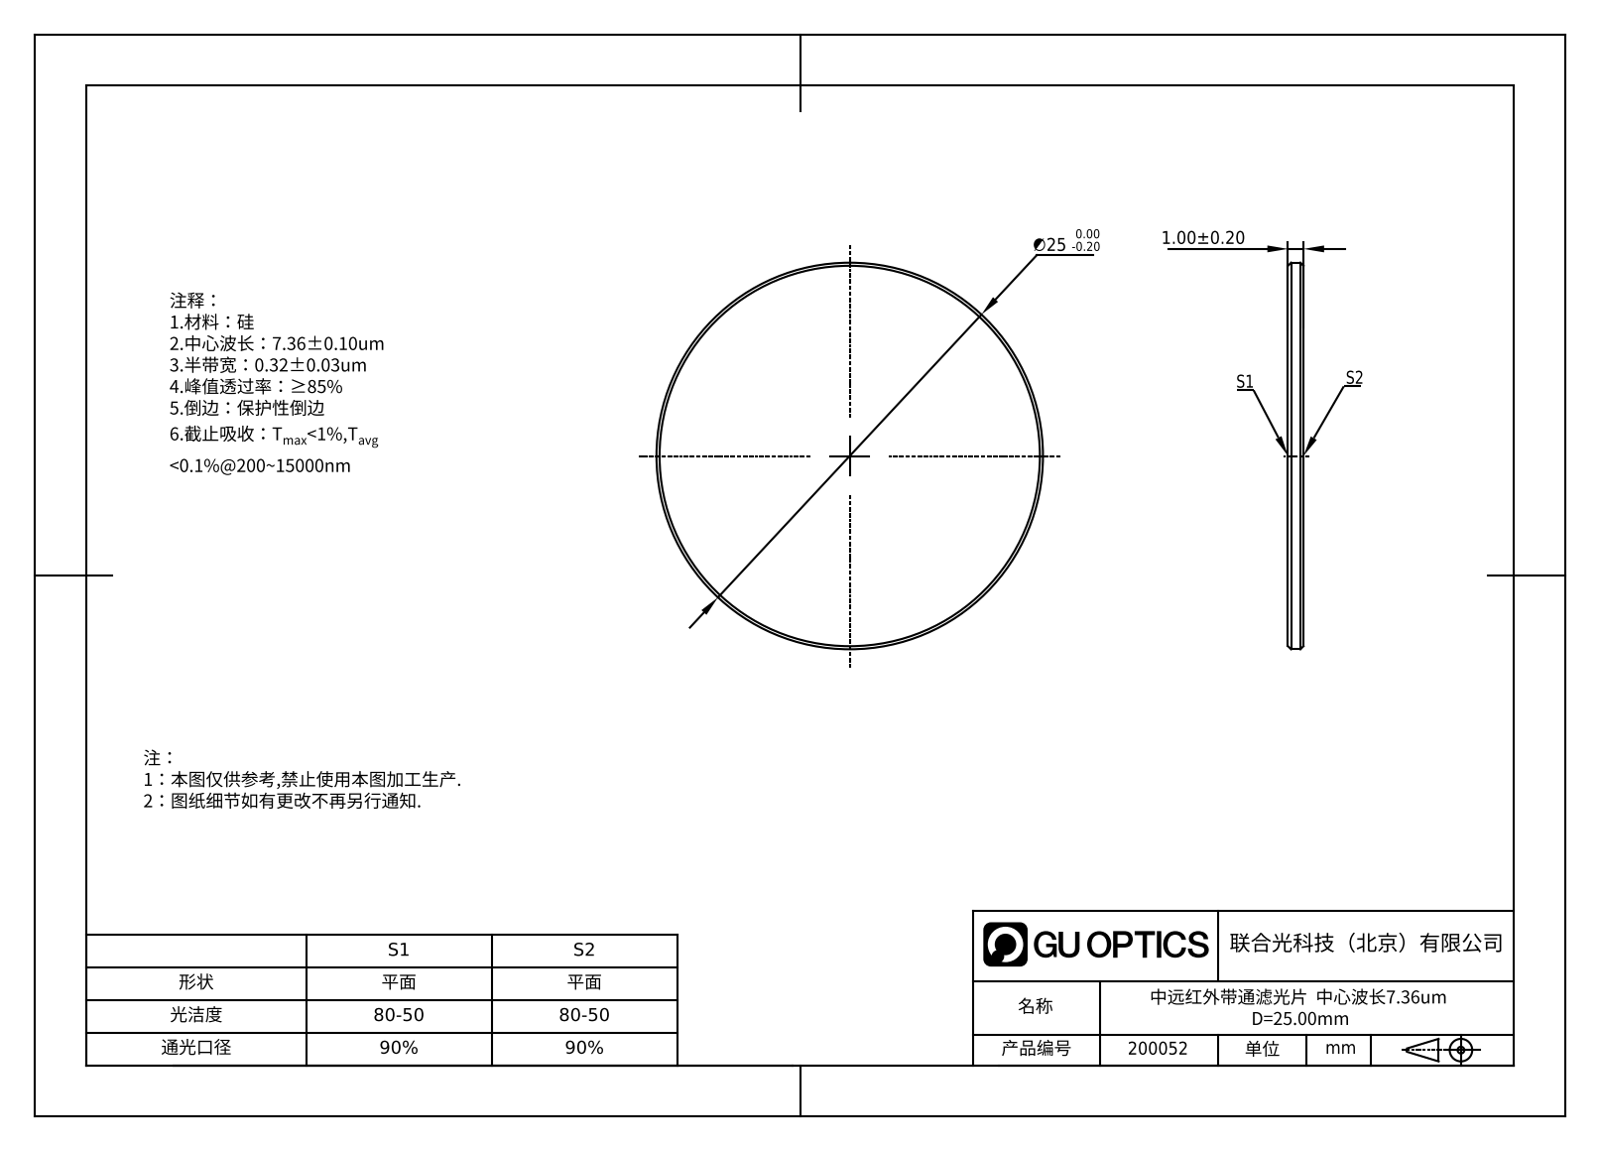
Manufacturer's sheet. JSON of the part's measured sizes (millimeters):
{"part_name": "GNIF-320-7360-D25", "step_written_by": "SolidWorks 2022 (AUTOMOTIVE_DESIGN)", "units": "millimeters", "bodies": {"solids": 1, "faces": 8, "planar": 2, "cylindrical": 2, "other": 4}, "overall_size": [25, 25, 1], "volume_mm3": 488, "surface_area_mm2": 1042, "round_bosses_or_shafts": [[25, 1]], "face_to_face_distances": [1]}
